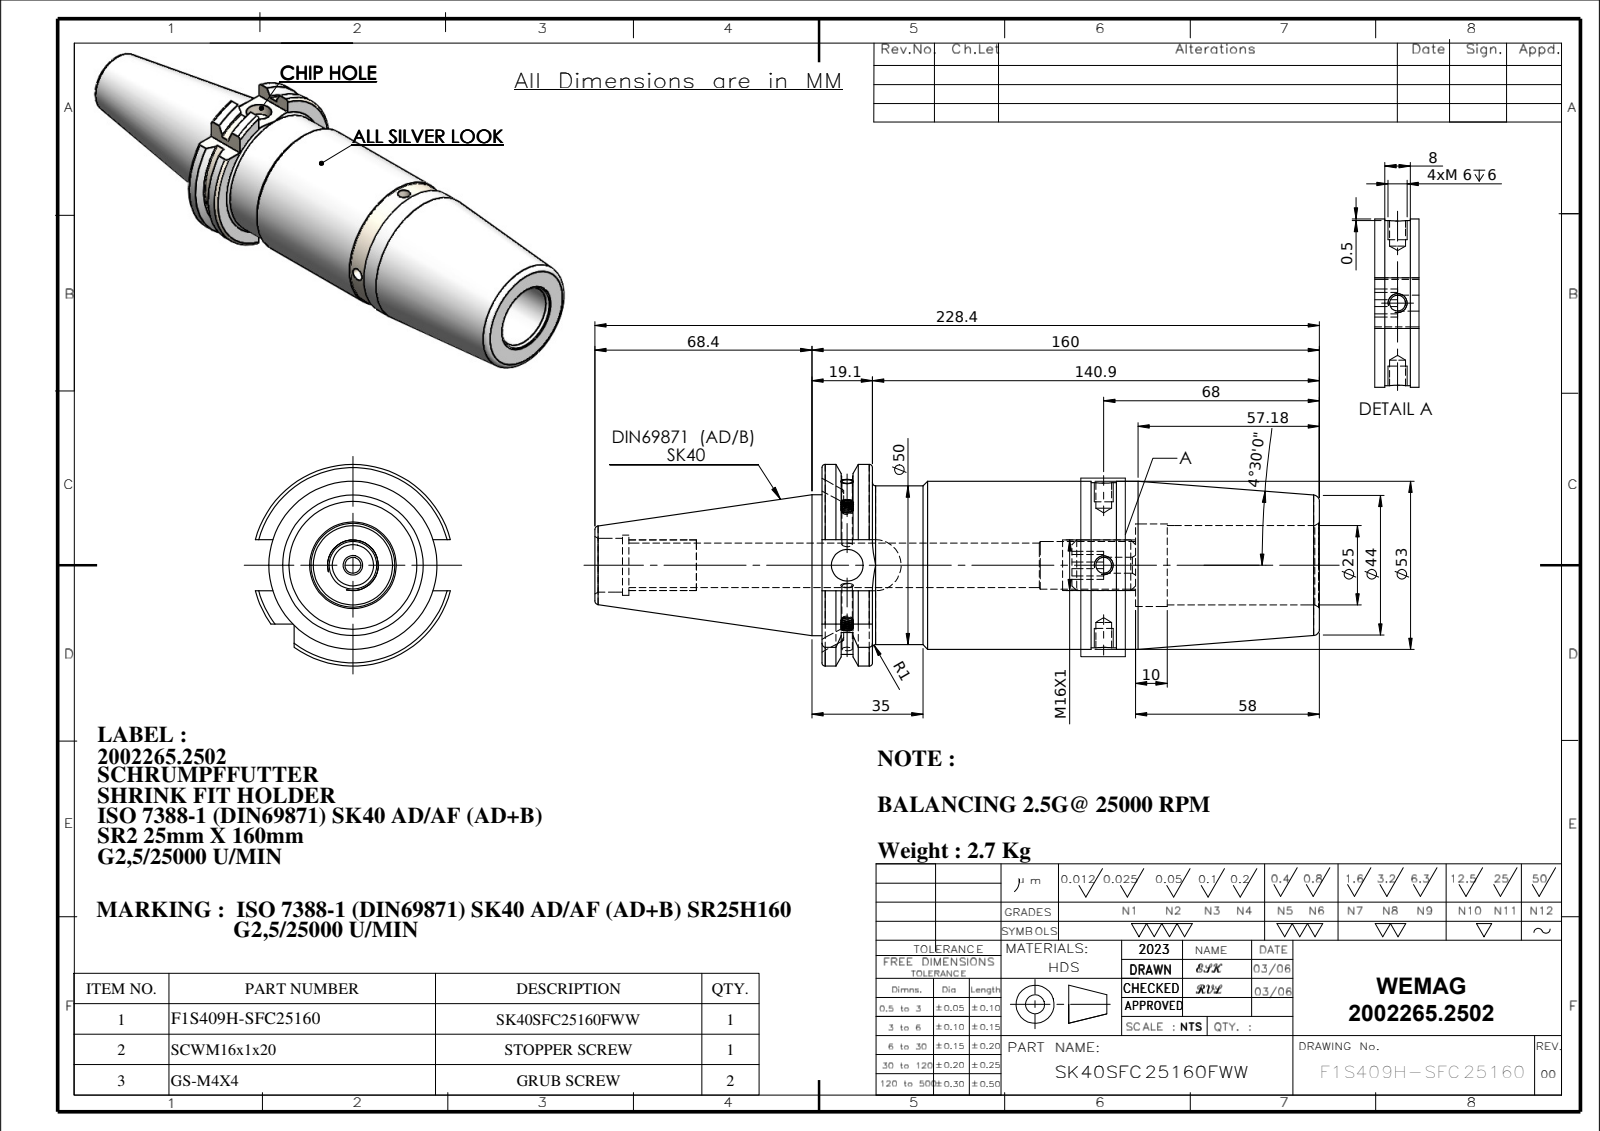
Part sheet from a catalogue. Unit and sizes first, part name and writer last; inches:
Units: inches
Overall size (bounding box): 8.992 × 2.502 × 2.42
Round holes (diameter × count): ⌀0.197 ×3, ⌀0.13 ×1, ⌀0.394 ×1, ⌀0.551 ×1, ⌀0.591 ×1, ⌀0.669 ×1, ⌀0.748 ×1, ⌀0.984 ×1, ⌀1.023 ×1
Round bosses / shafts (diameter × count): ⌀0.157 ×2, ⌀2.087 ×1, ⌀2.047 ×1, ⌀1.969 ×1, ⌀1.75 ×1, ⌀0.63 ×1
Partial cylindrical surfaces — rounded edges, fillets, slot ends (radius × count): R0.317 ×1, R1.107 ×1, R1.251 ×1
Main face-to-face distances: 6.173, 0.626, 5.547, 3.89, 3.264, 2.283, 1.882, 0.634, 0.236, 0.551
Hole centre spacings: 3.183
Volume: 21 in³ · Surface area: 84.08 in²
Bodies: 4 solids, 244 faces (60 planar, 74 cylindrical, 110 other)
Part name (STEP PRODUCT): SK40SFC25160FWW; SCWM16X1P; GS-M4X4_DIN 913 - M4 x 4-N; 91406-SR225160
STEP written by: SolidWorks 2018 (CONFIG_CONTROL_DESIGN)
